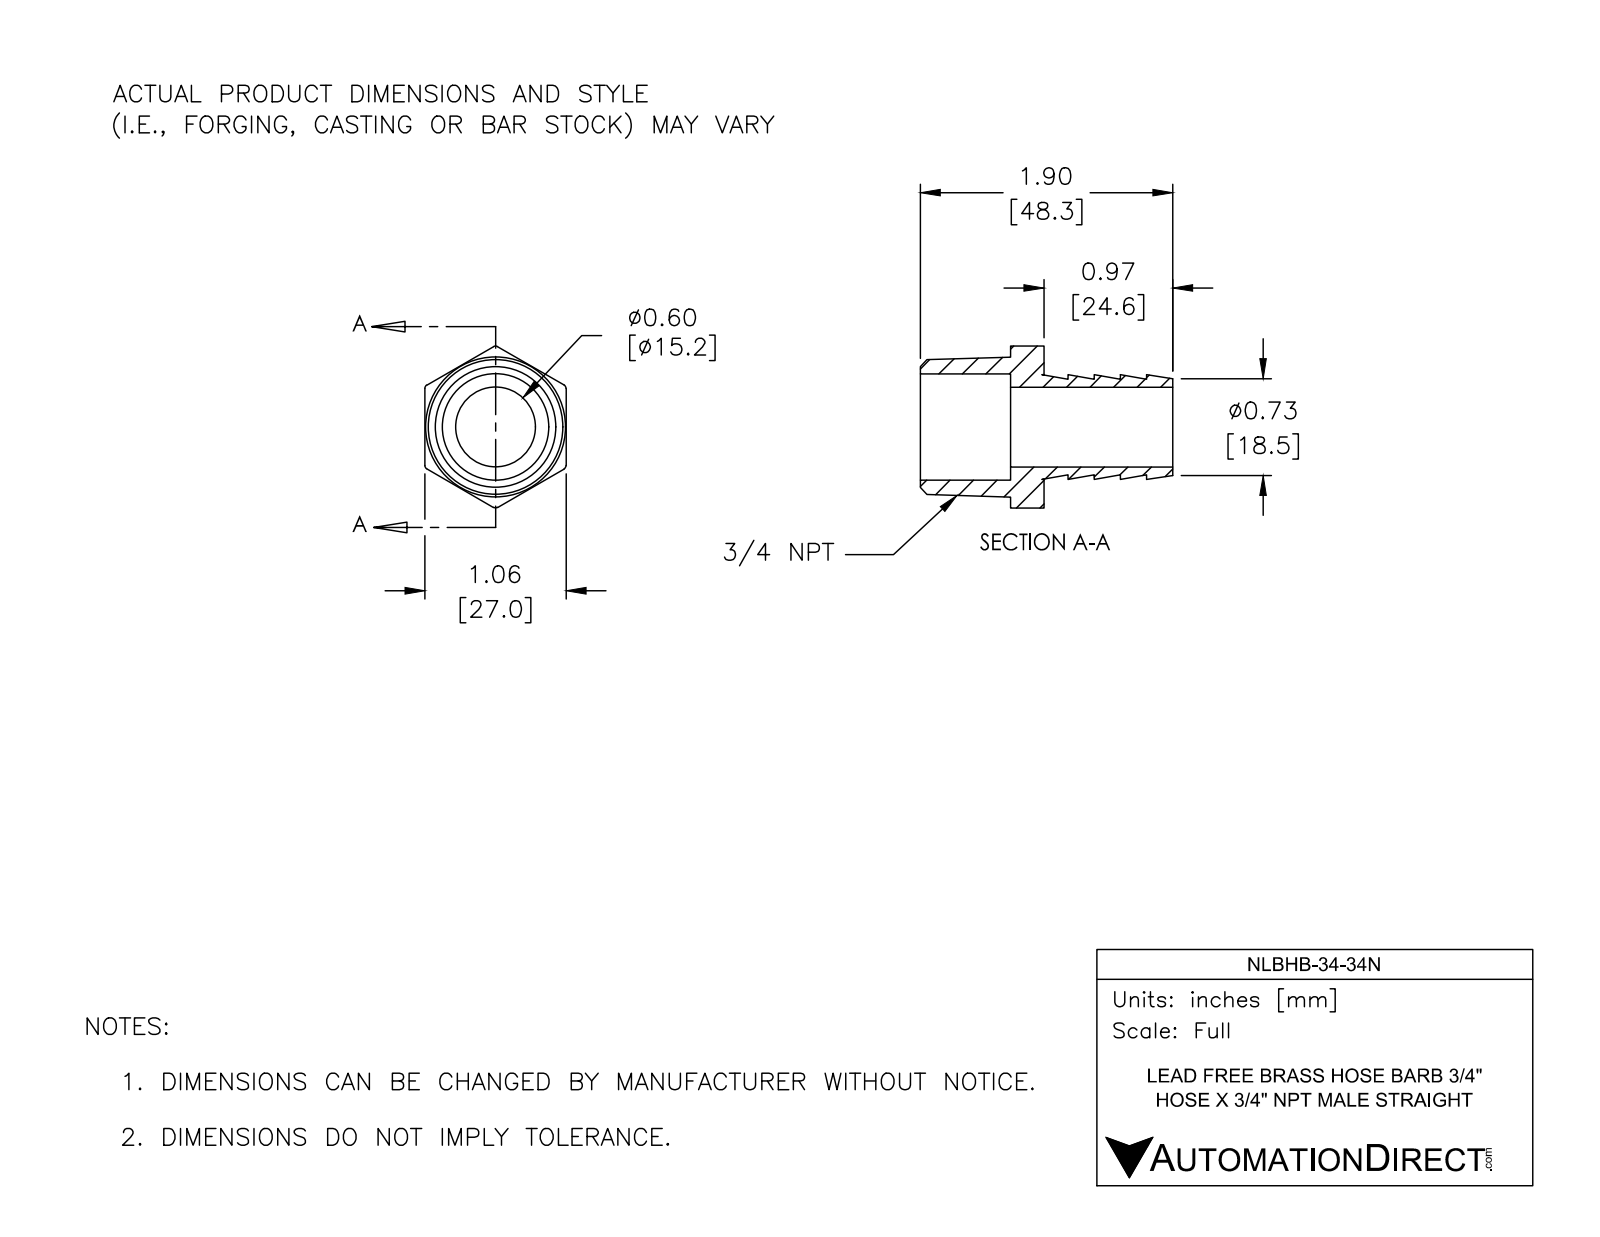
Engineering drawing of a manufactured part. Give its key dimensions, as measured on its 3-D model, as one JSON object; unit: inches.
{"part_name": "NLBHB-34-34N", "step_written_by": "SolidWorks 2017 (AUTOMOTIVE_DESIGN)", "units": "inches", "bodies": {"solids": 1, "faces": 41, "planar": 15, "cylindrical": 12, "other": 14}, "overall_size": [1.9, 1.218, 1.063], "volume_in3": 0.554, "surface_area_in2": 11, "round_holes": [[0.6, 1], [0.787, 1], [0.8, 1]], "partial_cylinders_radius": [[0.03, 6]], "face_to_face_distances": [1.062, 0.25, 0.197, 0.591, 0.394, 0.93, 0.68, 0.97, 1.22, 1.9]}
